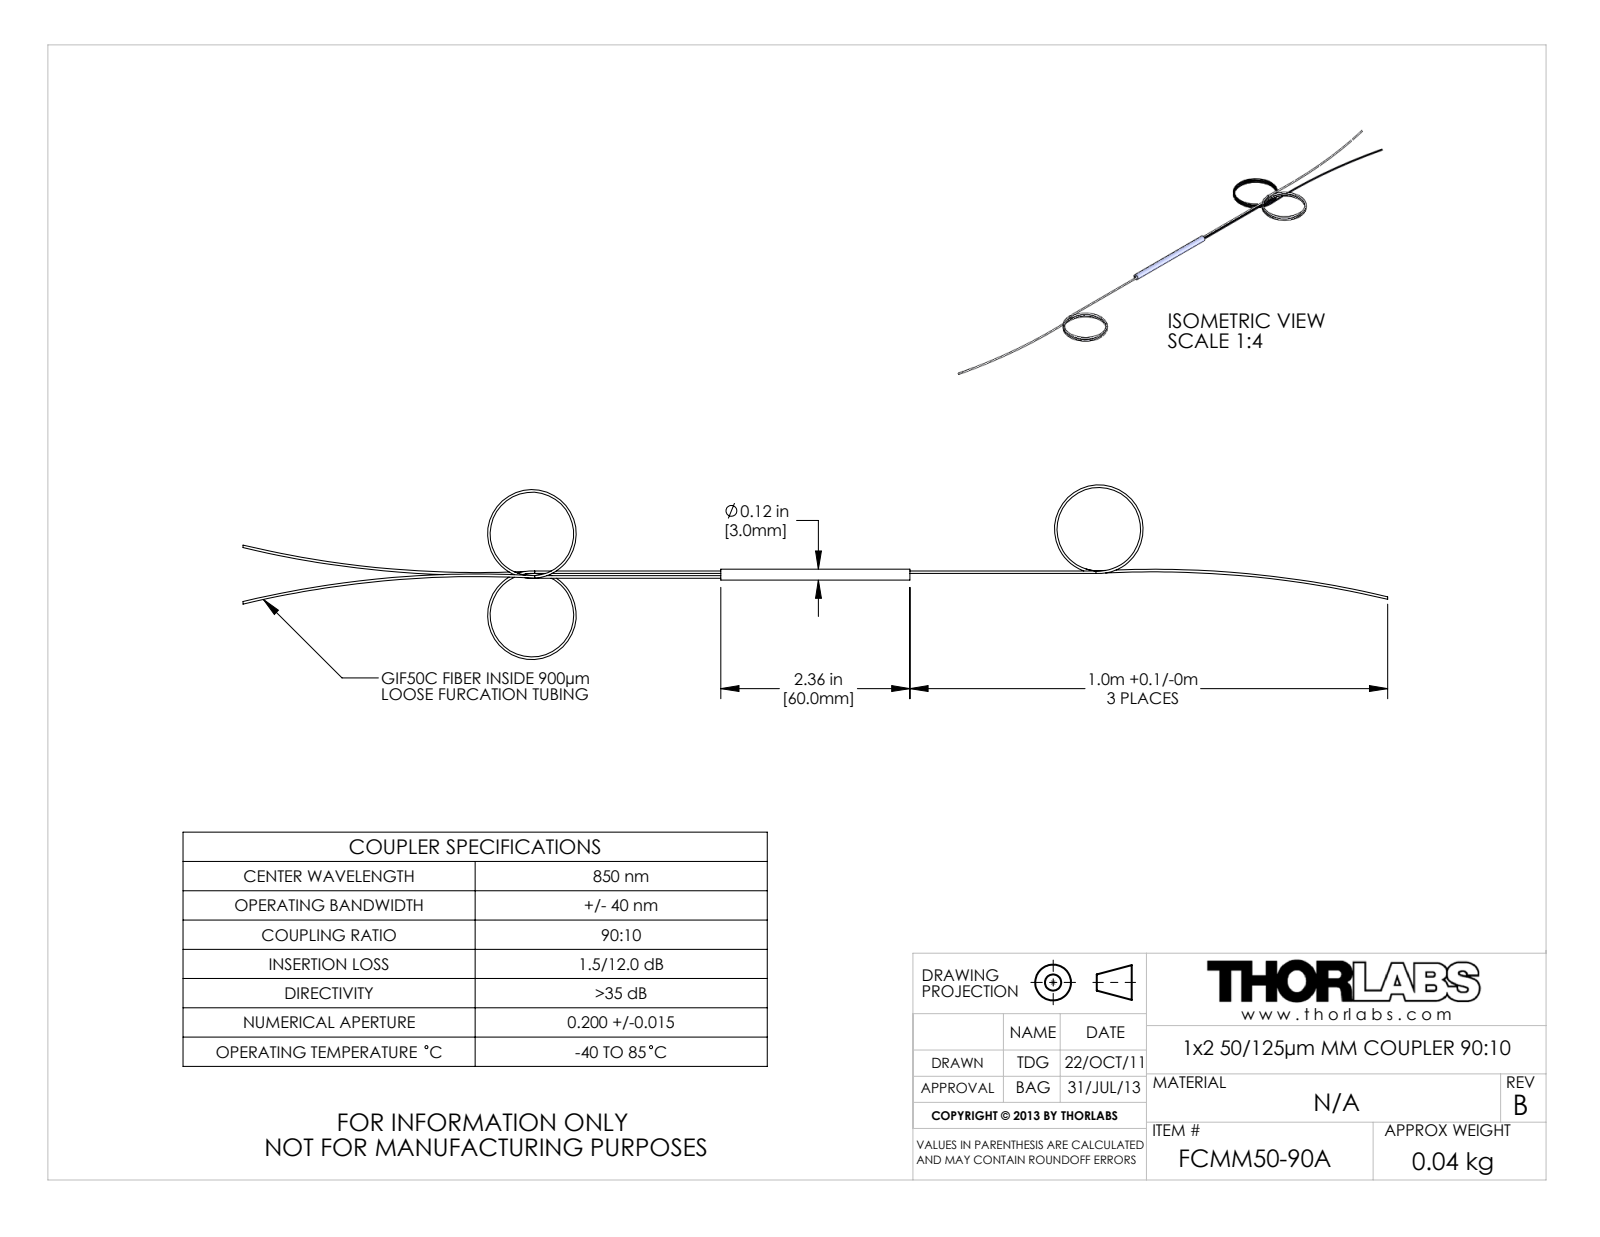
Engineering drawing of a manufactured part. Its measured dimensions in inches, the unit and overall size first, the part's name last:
Units: inches
Overall size (bounding box): 15.74 × 2.4 × 0.272
Round holes (diameter × count): ⌀0.039 ×2, ⌀0.13 ×1
Round bosses / shafts (diameter × count): ⌀0.035 ×2, ⌀0.15 ×1
Main face-to-face distances: 2.594, 2.598, 2.591, 6.571, 6.575, 9.165, 9.169, 7.949, 1.22, 1.378
Hole centre spacings: 0.033, 0.065
Volume: 0.068 in³ · Surface area: 8.722 in²
Bodies: 4 solids, 46 faces (10 planar, 18 cylindrical, 18 other)
Part name (STEP PRODUCT): 13897-E0W
STEP written by: SolidWorks 2012 (CONFIG_CONTROL_DESIGN)
